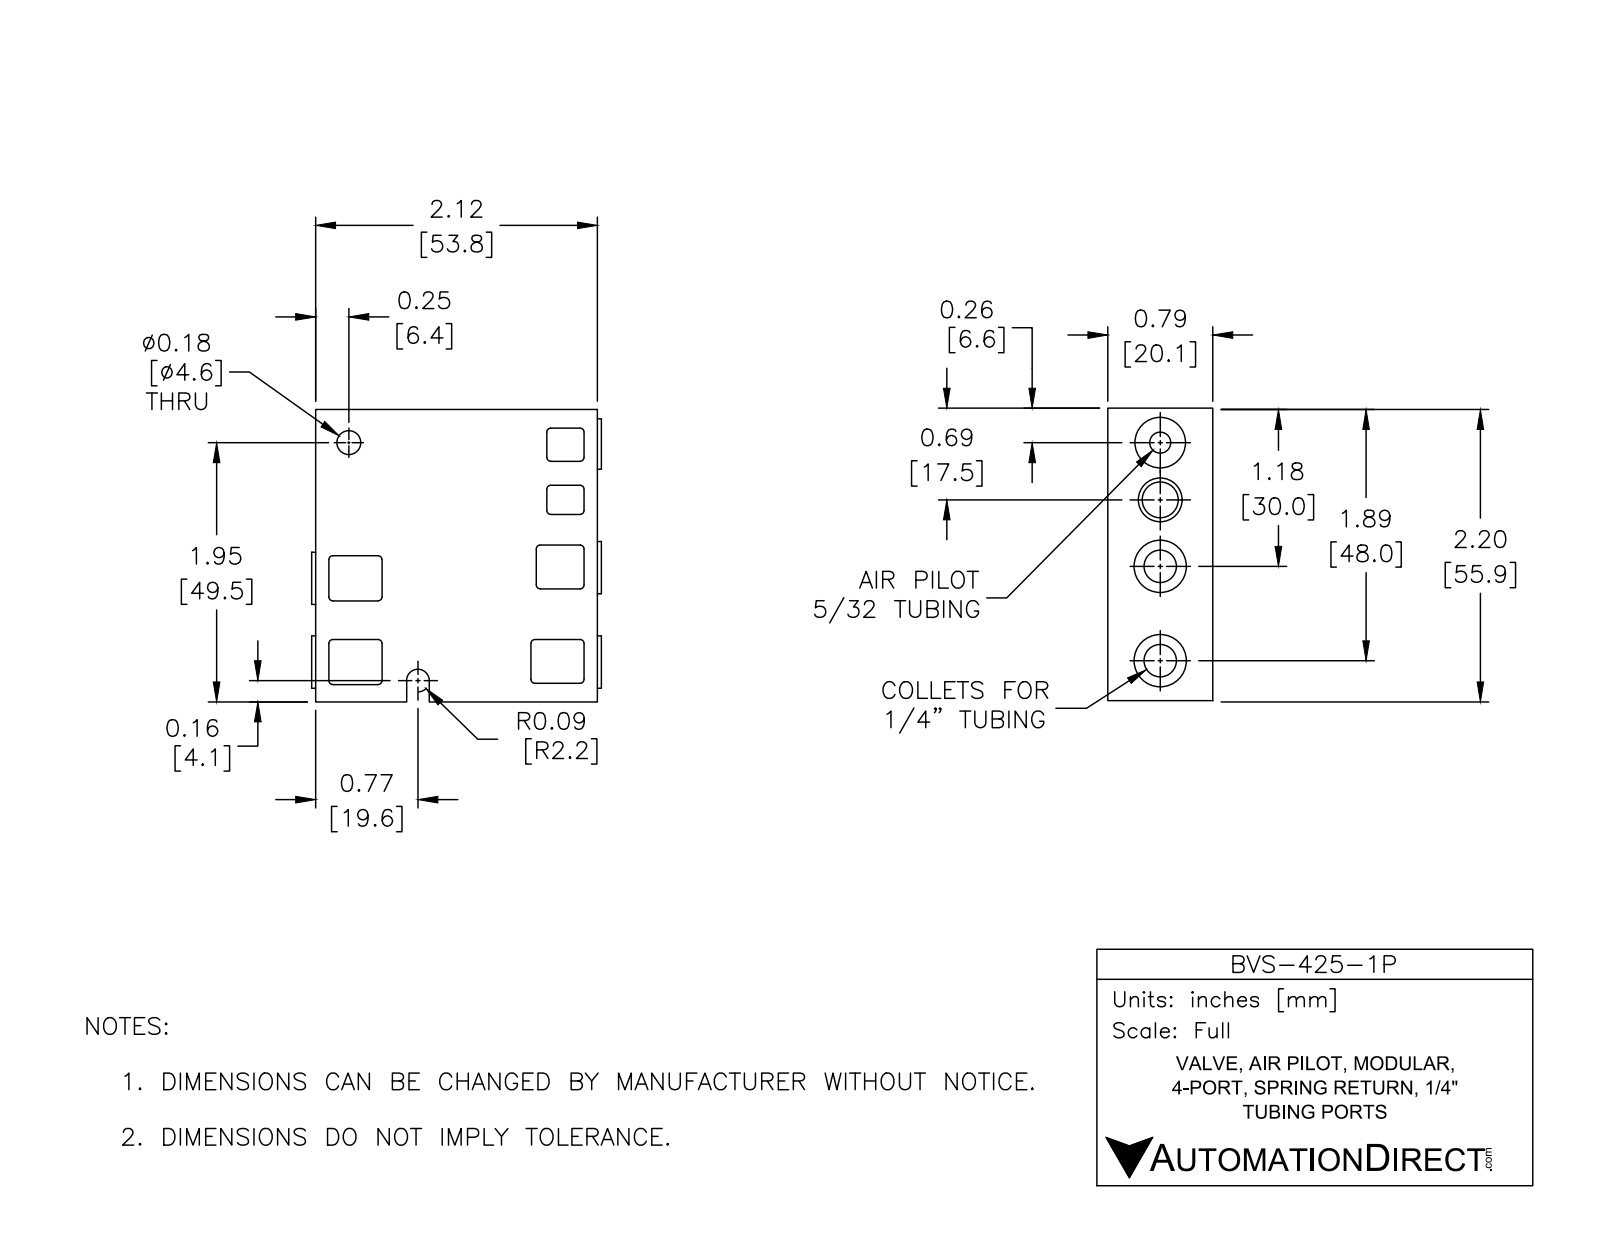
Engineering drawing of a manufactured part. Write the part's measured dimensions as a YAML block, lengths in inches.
part_name: "BVS-425-1P"
step_written_by: "SolidWorks 2016 (AUTOMOTIVE_DESIGN)"
units: inches
bodies: {solids: 1, faces: 158, planar: 81, cylindrical: 75, other: 2}
overall_size: [2.2, 2.18, 0.79]
volume: 3.361
surface_area: 21.23
round_holes:
  - {diameter: 0.254, count: 3}
  - {diameter: 0.06, count: 1}
  - {diameter: 0.16, count: 1}
  - {diameter: 0.18, count: 1}
round_bosses_or_shafts:
  - {diameter: 0.394, count: 3}
  - {diameter: 0.38, count: 1}
  - {diameter: 0.27, count: 1}
partial_cylinders:
  - {radius: 0.03, count: 24}
  - {radius: 0.085, count: 1}
face_to_face_distances: [0.79, 0.1, 2.2, 2.12, 0.69, 0.59, 0.03, 2.15, 0.13, 2.02]
hole_center_spacings: [0.08, 0.63, 0.71, 0.93, 1.01, 1.64]
